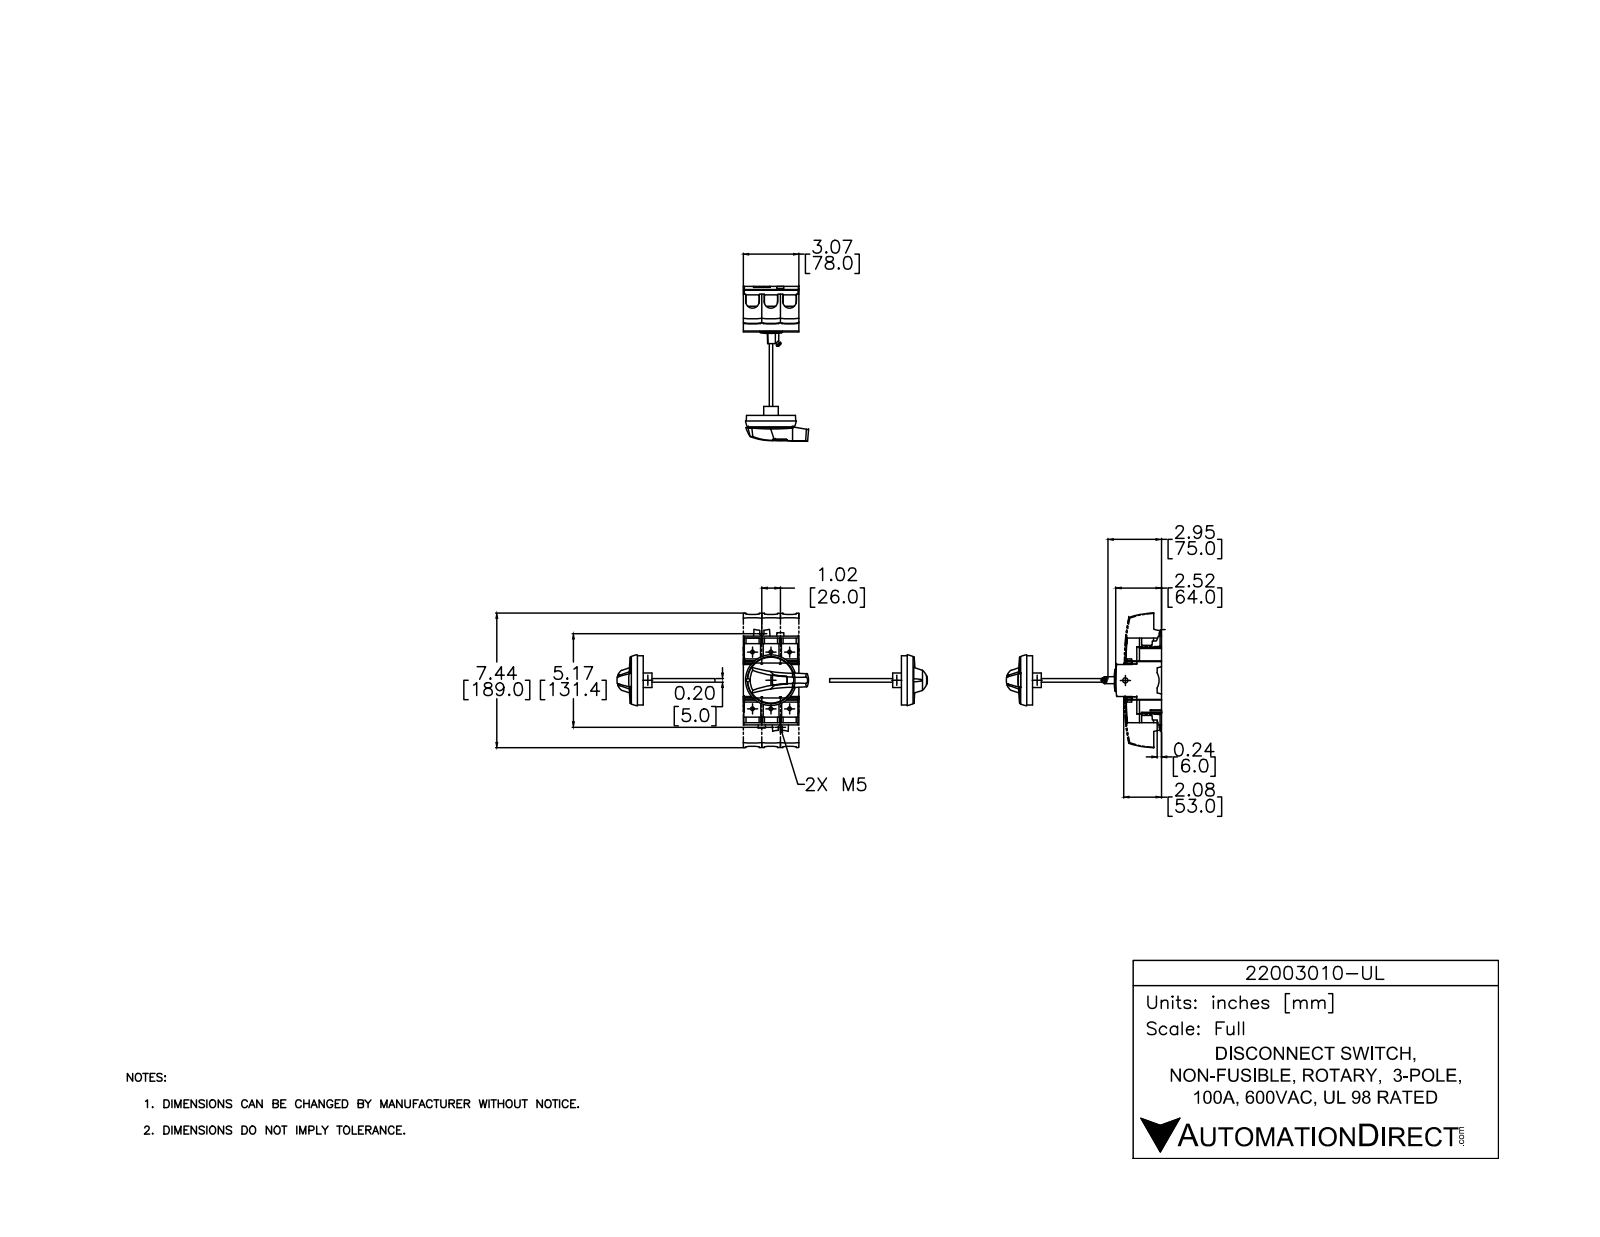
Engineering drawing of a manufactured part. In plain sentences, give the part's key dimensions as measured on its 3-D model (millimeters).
The part is named "22003010-UL". Its 3-D file was written by "SolidWorks 2015 (AUTOMOTIVE_DESIGN)". It is 1 solid with 274 faces: 210 planar, 45 cylindrical and 19 other. Overall it measures 142.7 by 78.8 by 64 millimeters. Its volume is 457 500 cubic millimeters and its surface area 53 740 square millimeters. Round holes: 6 of diameter 5.2, 1 of diameter 7.2, 1 of diameter 9.3, 1 of diameter 32. Round bosses or shafts: 1 of diameter 20.2. Partial cylindrical surfaces (rounded edges, fillets, slot ends): 3 of radius 90, 3 of radius 92.6, 2 of radius 2.9, 2 of radius 42.5. The main face-to-face distances are 77.8, 26, 7.9, 111, 1.1, 76.7, 2.5, 28.5, 46.9, 20.9. The hole center spacings are 26, 83.7, 79.6, 47.5, 47.5, 52, 95, 39.8.
